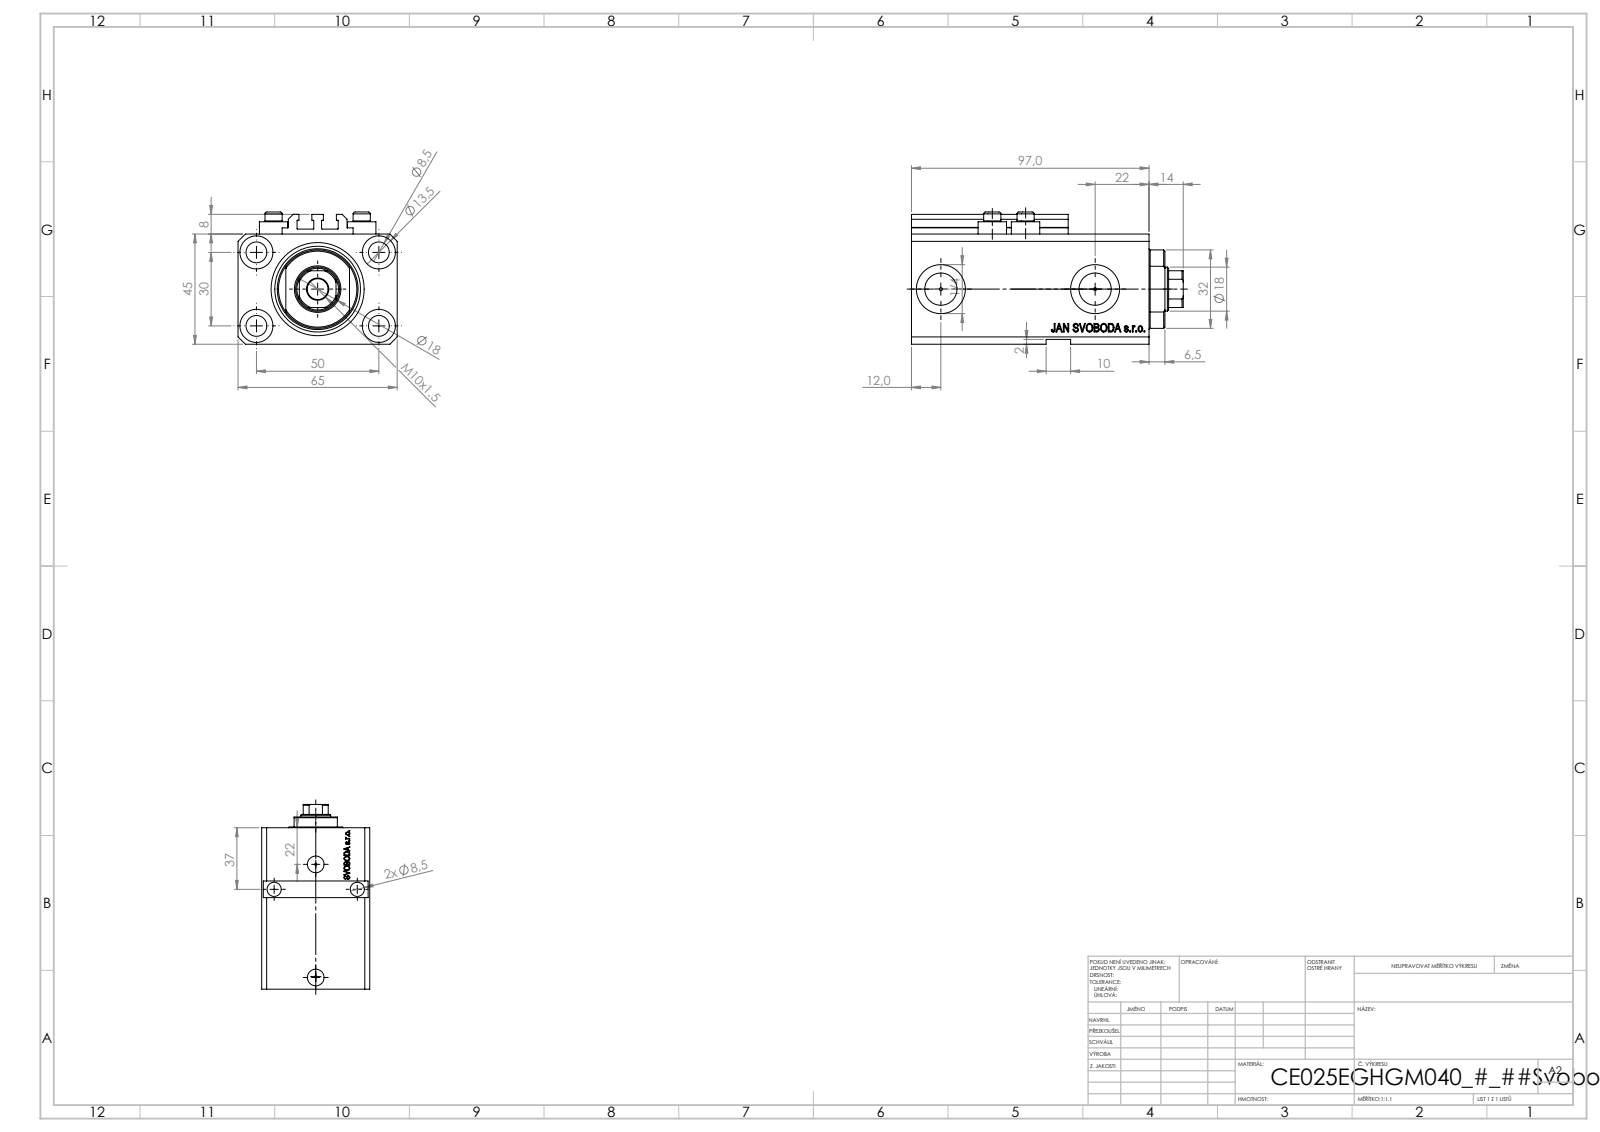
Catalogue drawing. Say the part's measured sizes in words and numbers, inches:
The part is named "V250CE_VC_E; V250CE_C_VCP; ALLEN BOLT V250CE; V250CE_E_Body". Its 3-D file was written by "SolidWorks 2019 (CONFIG_CONTROL_DESIGN)". It is 8 solids with 1067 faces: 511 planar, 126 cylindrical and 430 other. Overall it measures 4.37 by 2.559 by 2.126 inches. Its volume is 15.33 cubic inches and its surface area 109 square inches. Round holes: 7 of diameter 0.335, 4 of diameter 0.049, 4 of diameter 0.157, 4 of diameter 0.531, 2 of diameter 0.394, 2 of diameter 0.518, 2 of diameter 0.787, 1 of diameter 0.709, 1 of diameter 0.984, 1 of diameter 1.496. Round bosses or shafts: 4 of diameter 0.457, 4 of diameter 0.276. Partial cylindrical surfaces (rounded edges, fillets, slot ends): 10 of radius 0.008, 1 of radius 0.335, 1 of radius 0.63. The main face-to-face distances are 1.772, 2.559, 3.268, 0.551, 0.079, 3.819, 1.85, 0.272, 2.996, 3.547. The hole center spacings are 1.148, 1.969, 0.535, 0.595, 1.098, 1.181, 1.228, 1.245.
